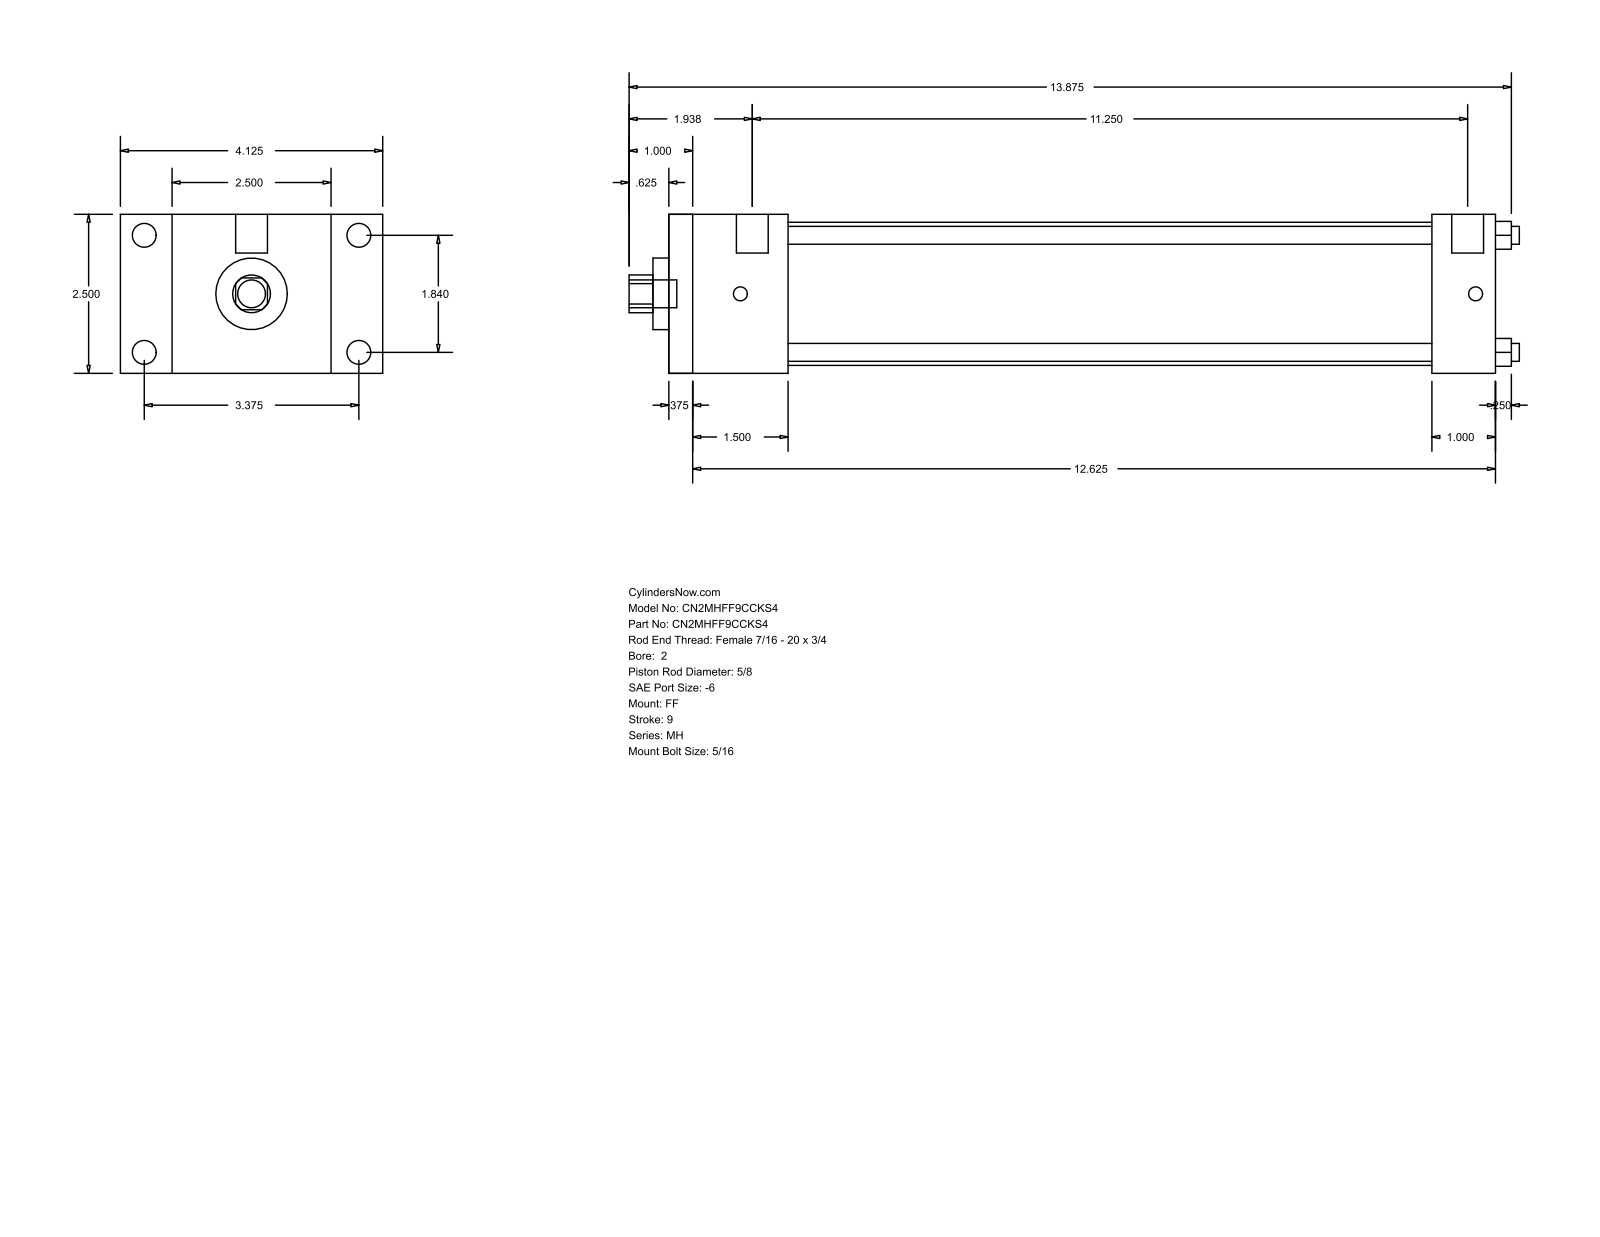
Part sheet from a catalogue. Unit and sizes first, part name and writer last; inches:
Units: inches
Overall size (bounding box): 14 × 4.125 × 2.5
Round holes (diameter × count): ⌀0.281 ×4, ⌀0.625 ×1, ⌀1.125 ×1, ⌀2.25 ×1
Round bosses / shafts (diameter × count): ⌀0.375 ×4, ⌀0.219 ×4, ⌀0.5 ×2, ⌀0.437 ×1
Partial cylindrical surfaces — rounded edges, fillets, slot ends (radius × count): R0.297 ×1
Main face-to-face distances: 2.5, 13, 0.375, 12.625, 1.5, 1.875, 12, 11.625, 10.125, 11.125
Hole centre spacings: 1.301, 1.84, 2.602
Bodies: 0 solids, 92 faces (64 planar, 28 cylindrical, 0 other)
Part name (STEP PRODUCT): MH_FF__0200_0.625
STEP written by: GSSL Pune (CONFIG_CONTROL_DESIGN)
